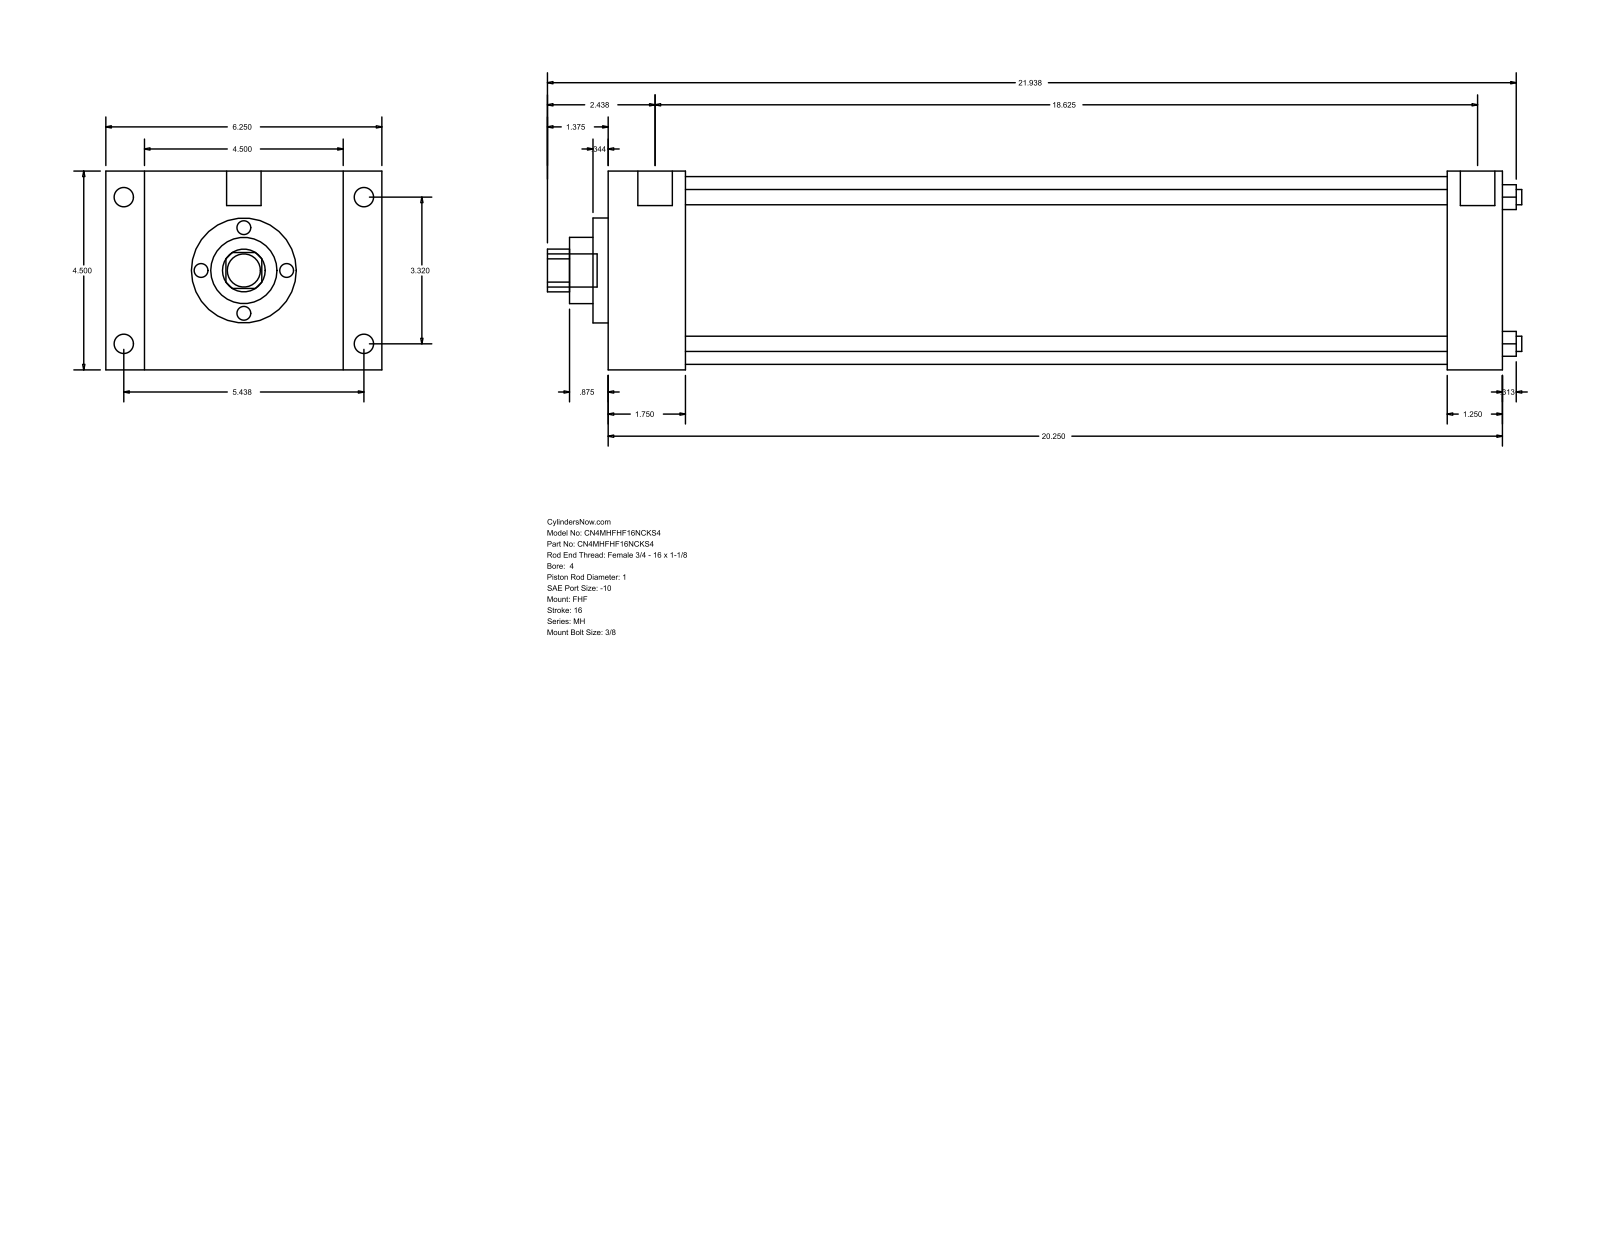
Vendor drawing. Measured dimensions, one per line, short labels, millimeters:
name: MH_FHF__0400_1
written by: GSSL Pune (CONFIG_CONTROL_DESIGN)
unit: mm
bodies: 0 solids, 90 faces (61 planar, 29 cylindrical, 0 other)
size: 560.39 × 158.75 × 114.3
holes: 4× ⌀8.76, 1× ⌀25.4, 1× ⌀38.1, 1× ⌀60.33, 1× ⌀107.95
bosses: 4× ⌀11.13, 4× ⌀8.73, 2× ⌀19.84, 1× ⌀19.05
rounds: 1× R12.29
face distances: 114.3, 514.35, 44.46, 469.89, 22.23, 136.53, 158.76, 482.6, 438.14, 31.75
hole spacings: 59.62, 84.32, 119.25
